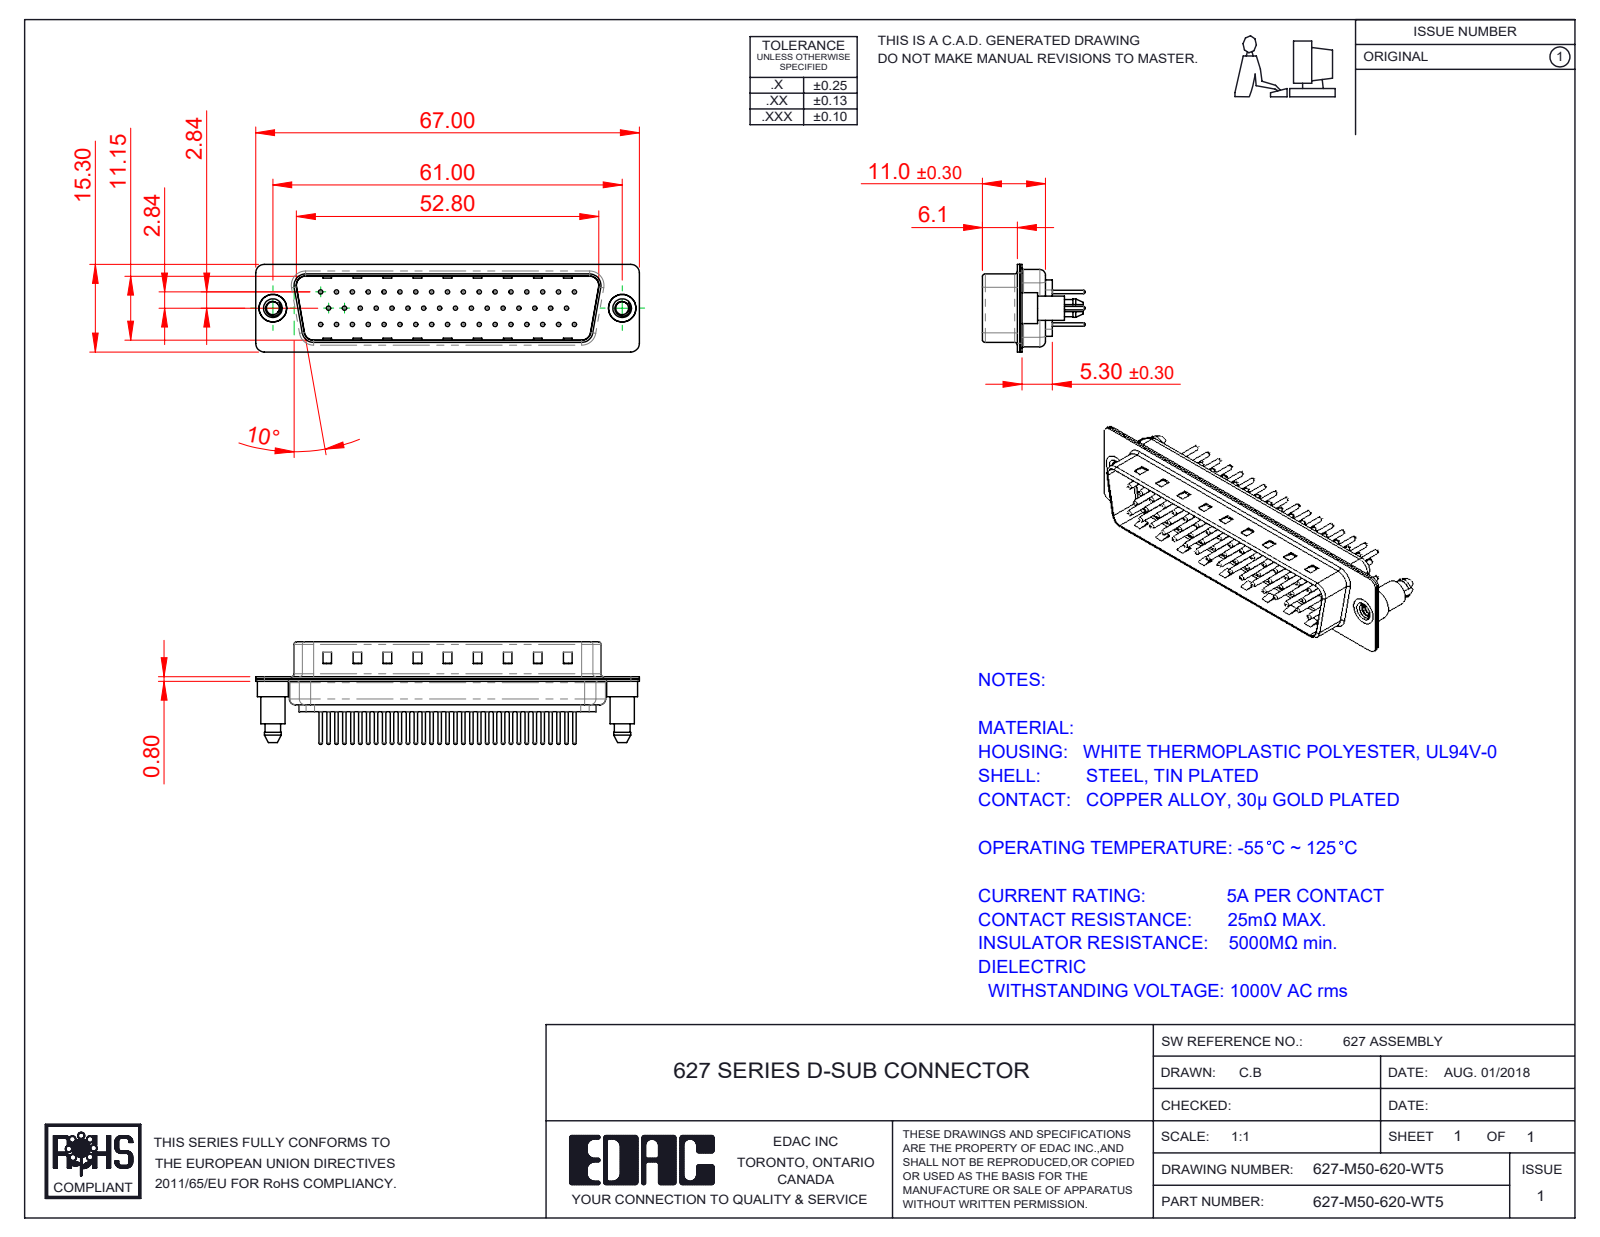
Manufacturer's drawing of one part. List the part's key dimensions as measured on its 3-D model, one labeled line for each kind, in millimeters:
Part name (STEP PRODUCT): 627M Contact Row 3_20; 627M 4-40 Threaded Boardlock; 627M Shell Front_50 Contacts; 627-M50-620-WT5 (+4 more)
STEP written by: SolidWorks 2020 (CONFIG_CONTROL_DESIGN)
Units: millimetres
Bodies: 55 solids, 2312 faces (569 planar, 873 cylindrical, 870 other)
Overall size (bounding box): 67 × 17.9 × 15.3
Volume: 4 659 mm³ · Surface area: 11 032 mm²
Round holes (diameter × count): ⌀0.75 ×50, ⌀1.6 ×50, ⌀2 ×50, ⌀2.26 ×2, ⌀4 ×2, ⌀4.8 ×2
Round bosses / shafts (diameter × count): ⌀1.5 ×50, ⌀0.6 ×50, ⌀5.4 ×2, ⌀4.9 ×2, ⌀4.25 ×2
Partial cylindrical surfaces — rounded edges, fillets, slot ends (radius × count): R1.5 ×18, R2 ×12, R1.6 ×10, R0.5 ×8, R0.25 ×4, R0.6 ×4, R0.65 ×4, R0.9 ×4
Main face-to-face distances: 0.4, 11.55, 5.7, 6.1, 0.78, 0.77, 12.33, 5.3, 12.32, 13.1
Hole centre spacings: 3.16, 2.77, 5.54, 8.31, 11.08, 13.85, 16.62, 5.03
